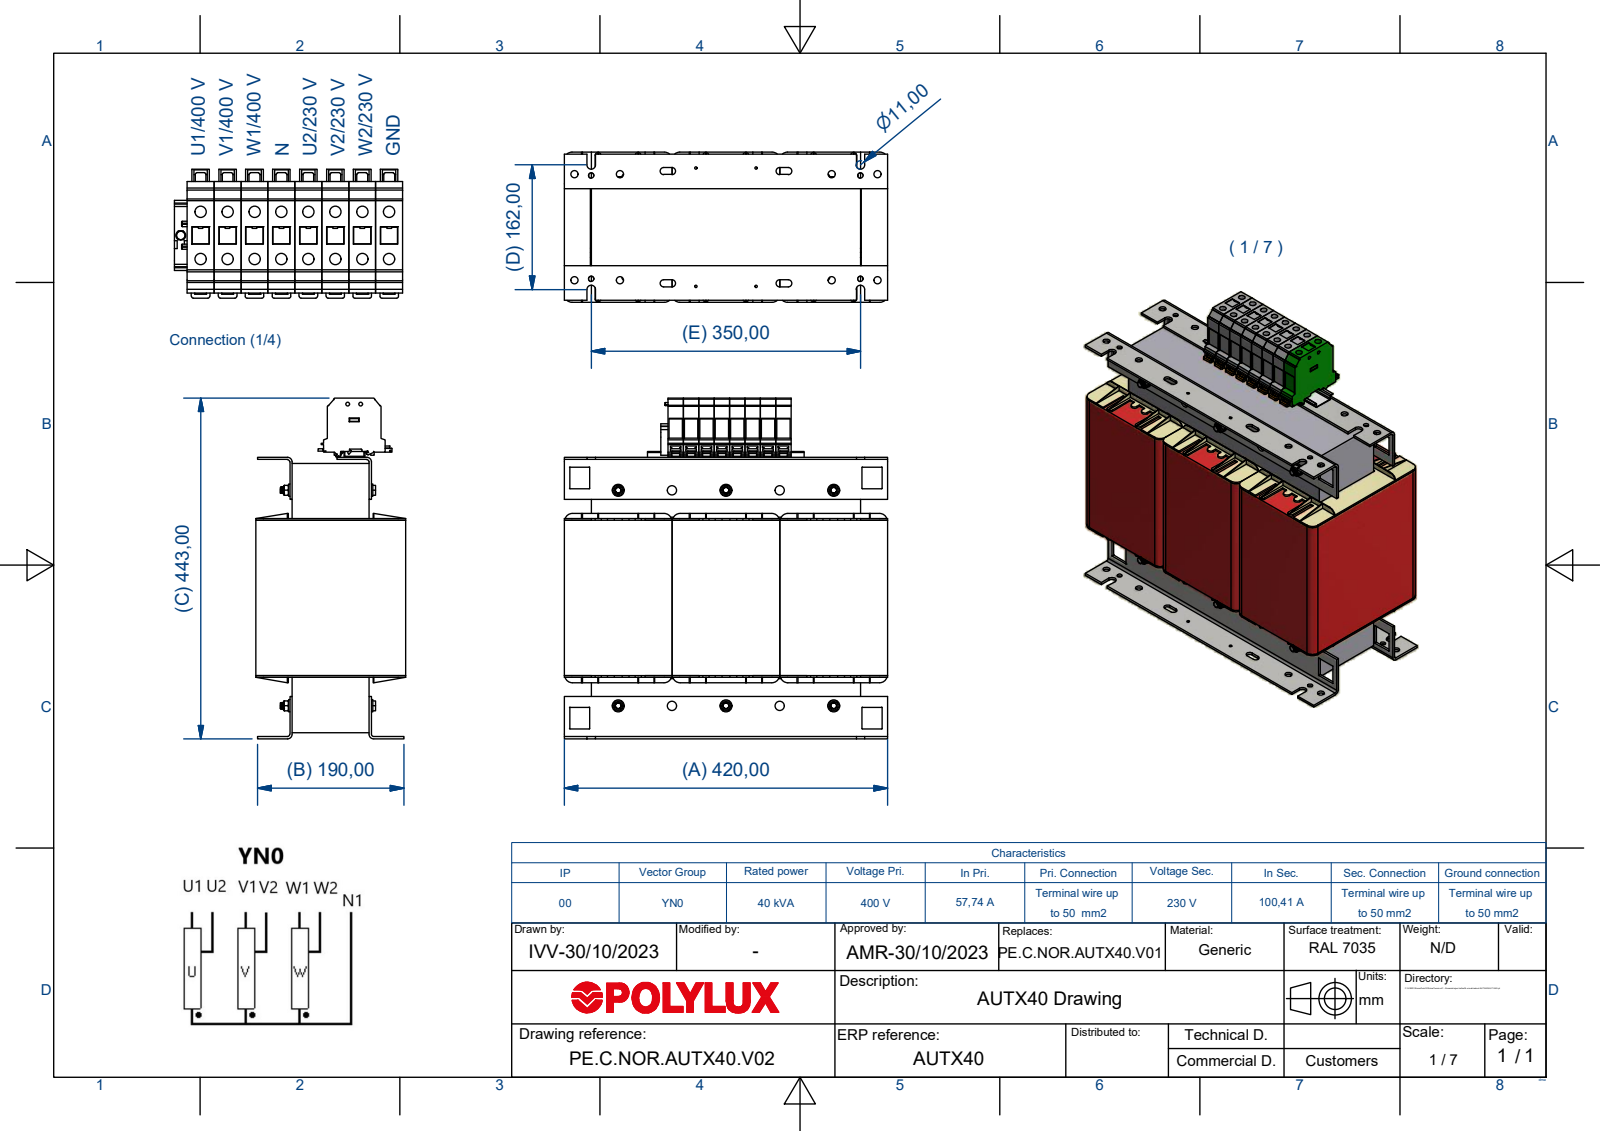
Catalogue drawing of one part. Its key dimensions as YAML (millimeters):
part_name: "AUTX40"
step_written_by: "Autodesk Inventor 2018 (AUTOMOTIVE_DESIGN)"
units: millimeters
bodies: {solids: 45, faces: 3789, planar: 2909, cylindrical: 790, other: 90}
overall_size: [442.9, 420, 195]
volume: 22780000
surface_area: 2395000
round_holes:
  - {diameter: 9, count: 18}
  - {diameter: 8.5, count: 16}
  - {diameter: 6.65, count: 12}
  - {diameter: 12, count: 10}
  - {diameter: 3.5, count: 6}
  - {diameter: 4.5, count: 2}
  - {diameter: 2, count: 1}
round_bosses_or_shafts:
  - {diameter: 16, count: 6}
  - {diameter: 8, count: 6}
  - {diameter: 4, count: 2}
partial_cylinders:
  - {radius: 1, count: 51}
  - {radius: 4.5, count: 24}
  - {radius: 10, count: 24}
  - {radius: 0.5, count: 22}
  - {radius: 1.5, count: 16}
  - {radius: 2, count: 15}
  - {radius: 4, count: 12}
  - {radius: 5.5, count: 6}
face_to_face_distances: [3, 140, 2, 103, 32, 108, 280, 106, 1, 172]
hole_center_spacings: [350, 70, 103, 288.62, 35, 280, 22.09, 37.55]
